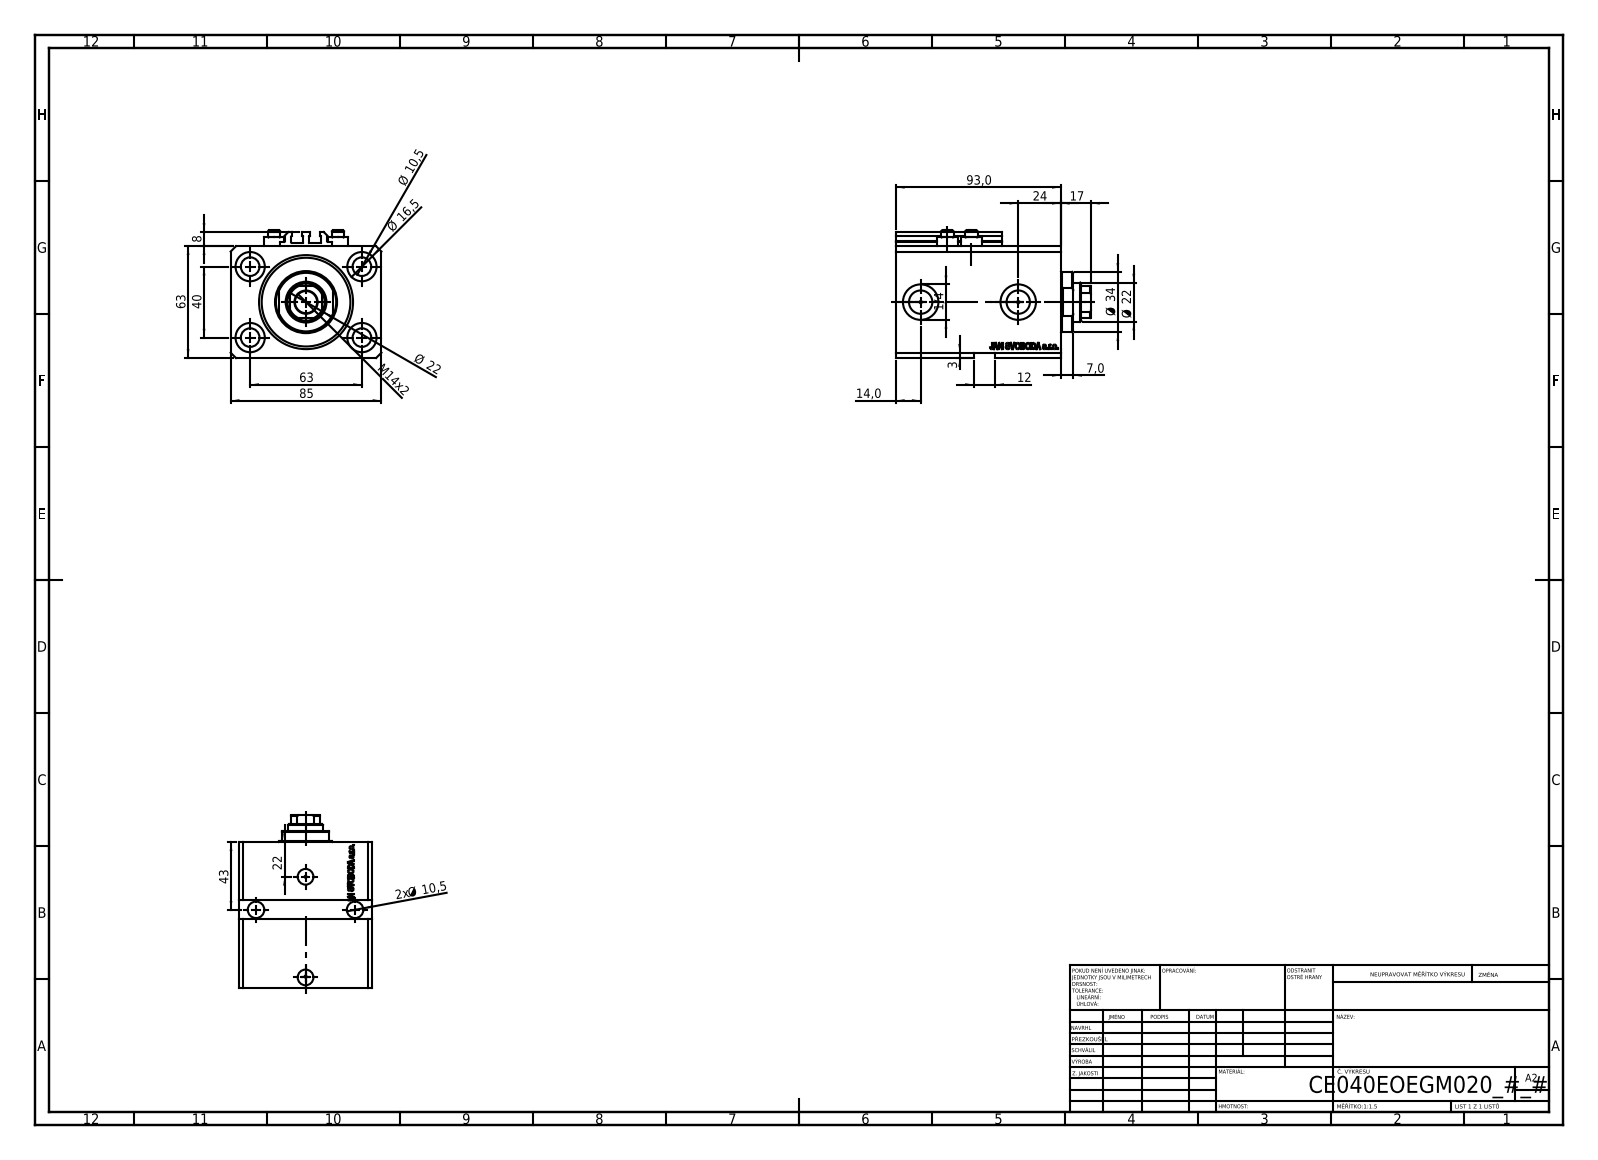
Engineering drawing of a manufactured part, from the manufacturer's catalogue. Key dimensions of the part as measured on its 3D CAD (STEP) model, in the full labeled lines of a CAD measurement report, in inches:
Part name (STEP PRODUCT): V250CE_VC_E; V250CE_E_Body; V250CE_C_VCP; ALLEN BOLT V250CE
STEP written by: SolidWorks 2019 (CONFIG_CONTROL_DESIGN)
Units: inches
Bodies: 8 solids, 1087 faces (535 planar, 126 cylindrical, 426 other)
Overall size (bounding box): 4.331 × 3.346 × 2.835
Volume: 26.68 in³ · Surface area: 148.5 in²
Round holes (diameter × count): ⌀0.413 ×6, ⌀0.049 ×4, ⌀0.157 ×4, ⌀0.65 ×4, ⌀0.394 ×2, ⌀0.518 ×2, ⌀0.787 ×2, ⌀0.492 ×1, ⌀0.866 ×1, ⌀1.575 ×1, ⌀2.087 ×1
Round bosses / shafts (diameter × count): ⌀0.457 ×4, ⌀0.276 ×4, ⌀1.339 ×1
Partial cylindrical surfaces — rounded edges, fillets, slot ends (radius × count): R0.008 ×10, R0.413 ×1
Main face-to-face distances: 2.48, 3.346, 3.661, 0.669, 2.992, 0.449, 2.543, 3.213, 0.118, 2.559
Hole centre spacings: 1.469, 2.48, 0.535, 0.606, 0.983, 1.103, 1.119, 1.324
